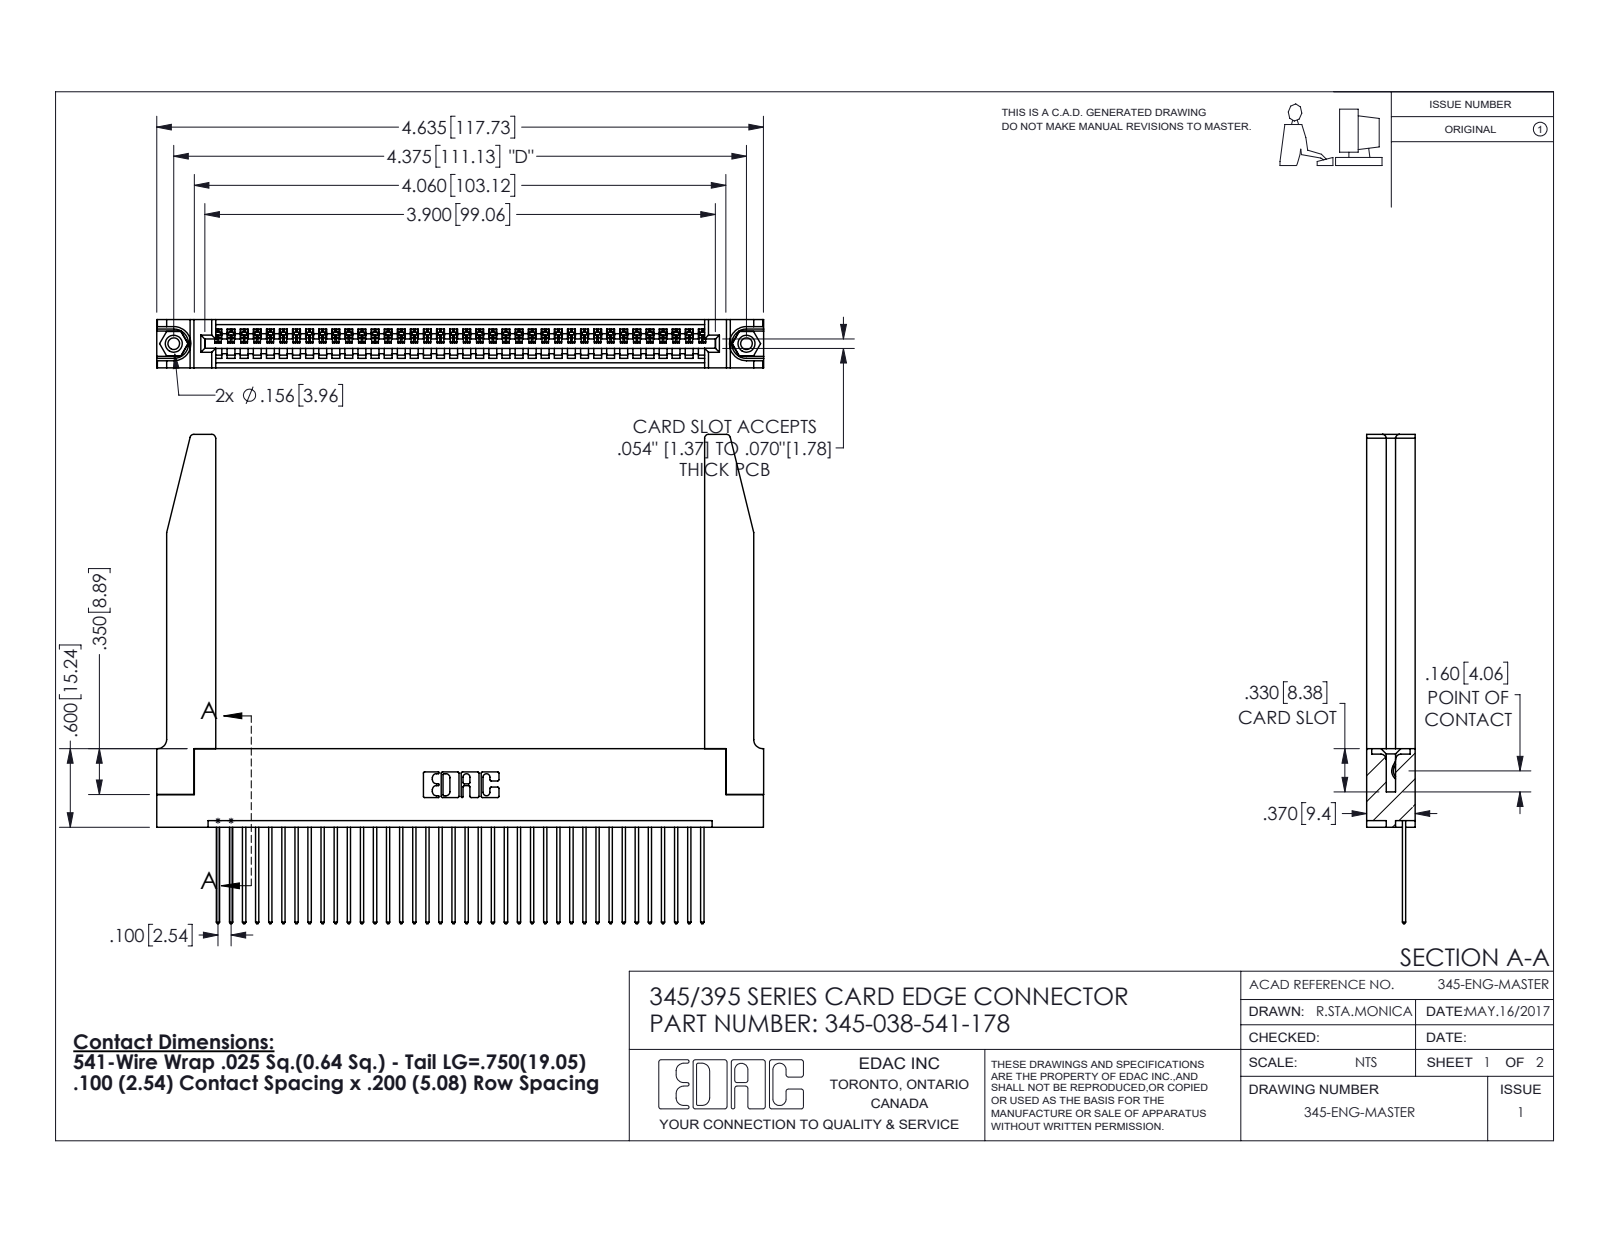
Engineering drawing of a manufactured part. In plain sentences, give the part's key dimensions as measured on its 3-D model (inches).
The part is named "345-250-001_345-250-001-102; 345-038-541-178; 345 Part_Flush Mounting Lugs - 0.156 Dia-TH; 345-220-078_345-220-078 (+1 more)". Its 3-D file was written by "SolidWorks 2016 (CONFIG_CONTROL_DESIGN)". It is 43 solids with 2564 faces: 1742 planar, 770 cylindrical and 52 other. Overall it measures 4.636 by 3.737 by 0.37 inches. Its volume is 1.162 cubic inches and its surface area 34.9 square inches. Round holes: 2 of diameter 0.089, 2 of diameter 0.125, 2 of diameter 0.156, 1 of diameter 0.064. Round bosses or shafts: 2 of diameter 0.155. Partial cylindrical surfaces (rounded edges, fillets, slot ends): 76 of radius 0.006, 76 of radius 0.01, 22 of radius 0.01, 8 of radius 0.03, 6 of radius 0.007, 6 of radius 0.031, 3 of radius 0.026, 2 of radius 0.031. The main face-to-face distances are 0.37, 0.072, 0.298, 0.098, 0.272, 0.025, 0.2, 0.225, 0.148, 0.15. The hole center spacings are 0.27, 4.139, 4.375.
